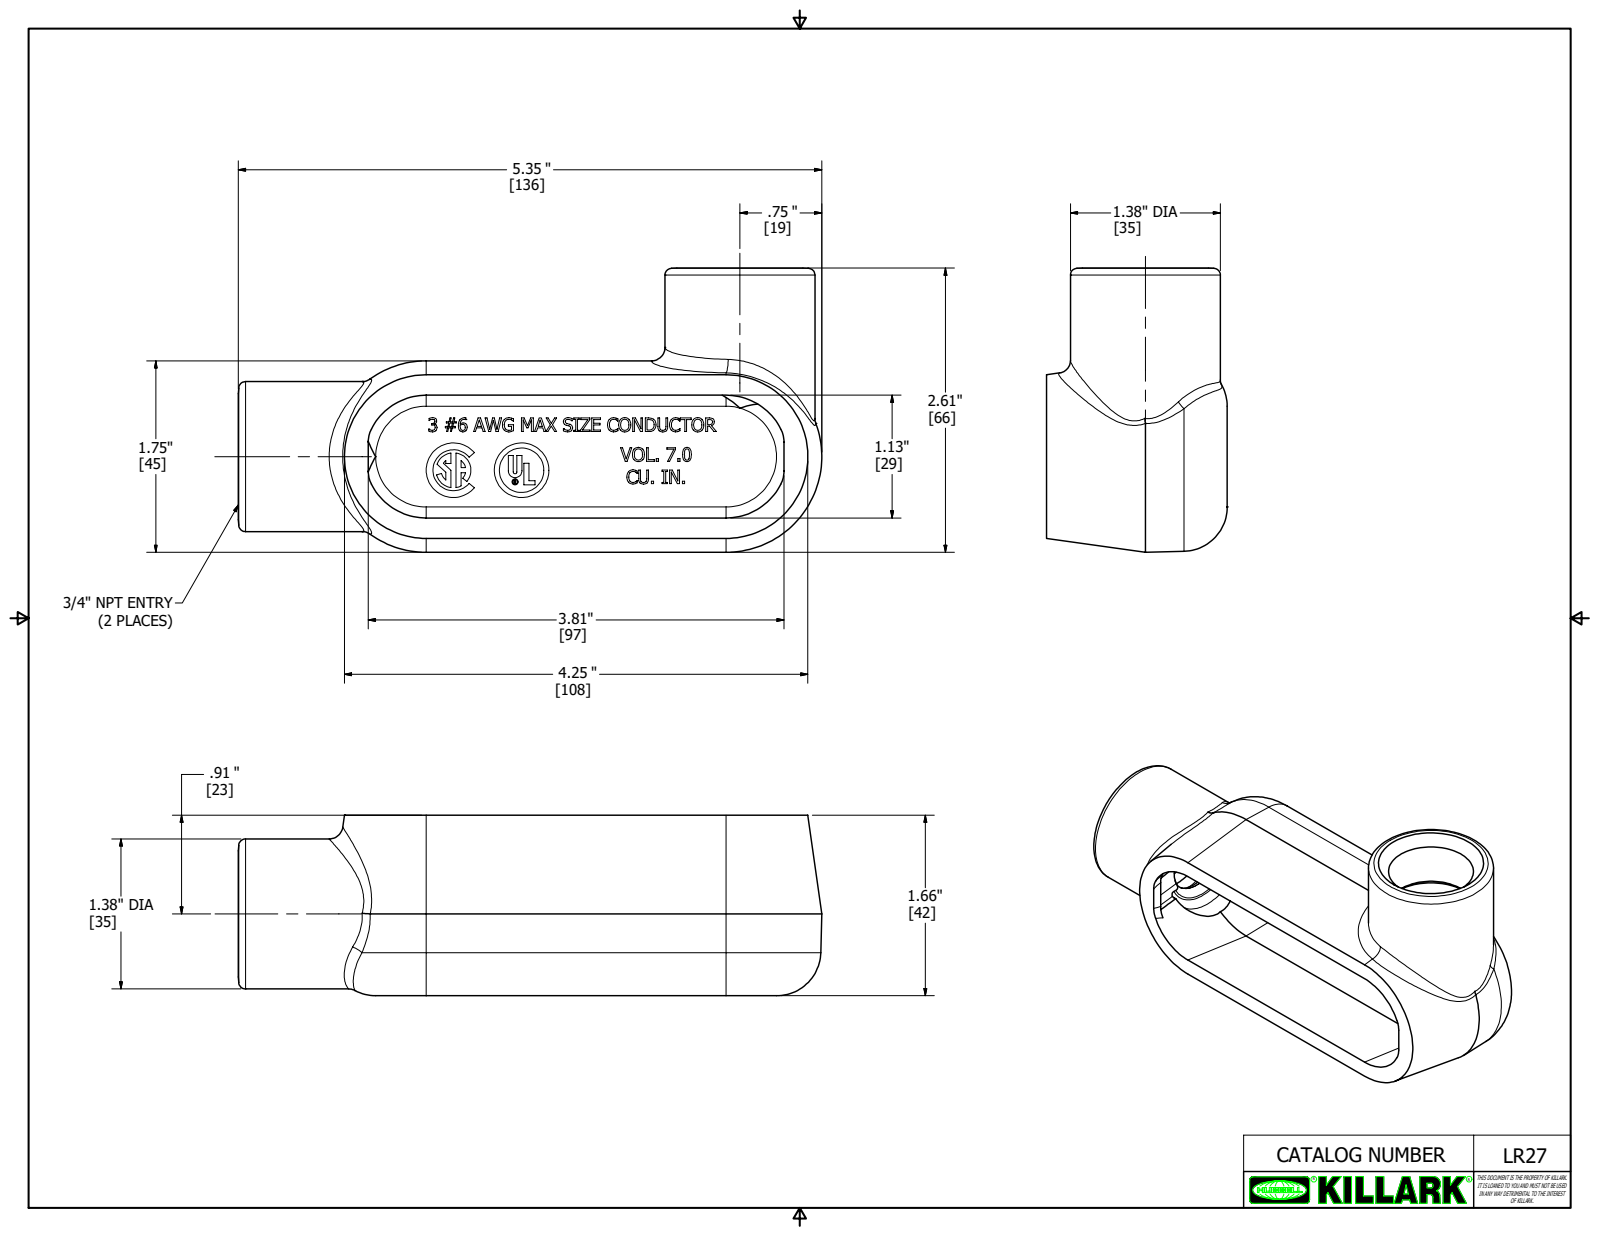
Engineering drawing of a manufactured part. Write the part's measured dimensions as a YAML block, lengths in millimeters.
part_name: "17657-2"
step_written_by: "Autodesk Inventor 2018 (AUTOMOTIVE_DESIGN)"
units: millimeters
bodies: {solids: 1, faces: 814, planar: 498, cylindrical: 36, other: 280}
overall_size: [135.9, 66.2, 42.1]
volume: 82050
surface_area: 37260
round_holes:
  - {diameter: 26.8, count: 2}
  - {diameter: 1.2, count: 1}
  - {diameter: 10.3, count: 1}
  - {diameter: 28.6, count: 1}
round_bosses_or_shafts:
  - {diameter: 34.9, count: 2}
  - {diameter: 12.7, count: 1}
  - {diameter: 1.4, count: 1}
partial_cylinders:
  - {radius: 1.6, count: 4}
  - {radius: 3.2, count: 4}
  - {radius: 5.6, count: 2}
  - {radius: 10.3, count: 2}
  - {radius: 0.2, count: 1}
  - {radius: 0.2, count: 1}
  - {radius: 0.4, count: 1}
  - {radius: 1.6, count: 1}
face_to_face_distances: [4.7, 4.7, 4.8, 42.1, 37.3, 4, 0.8, 41.3, 0.8, 5.6]
hole_center_spacings: [3.1]
